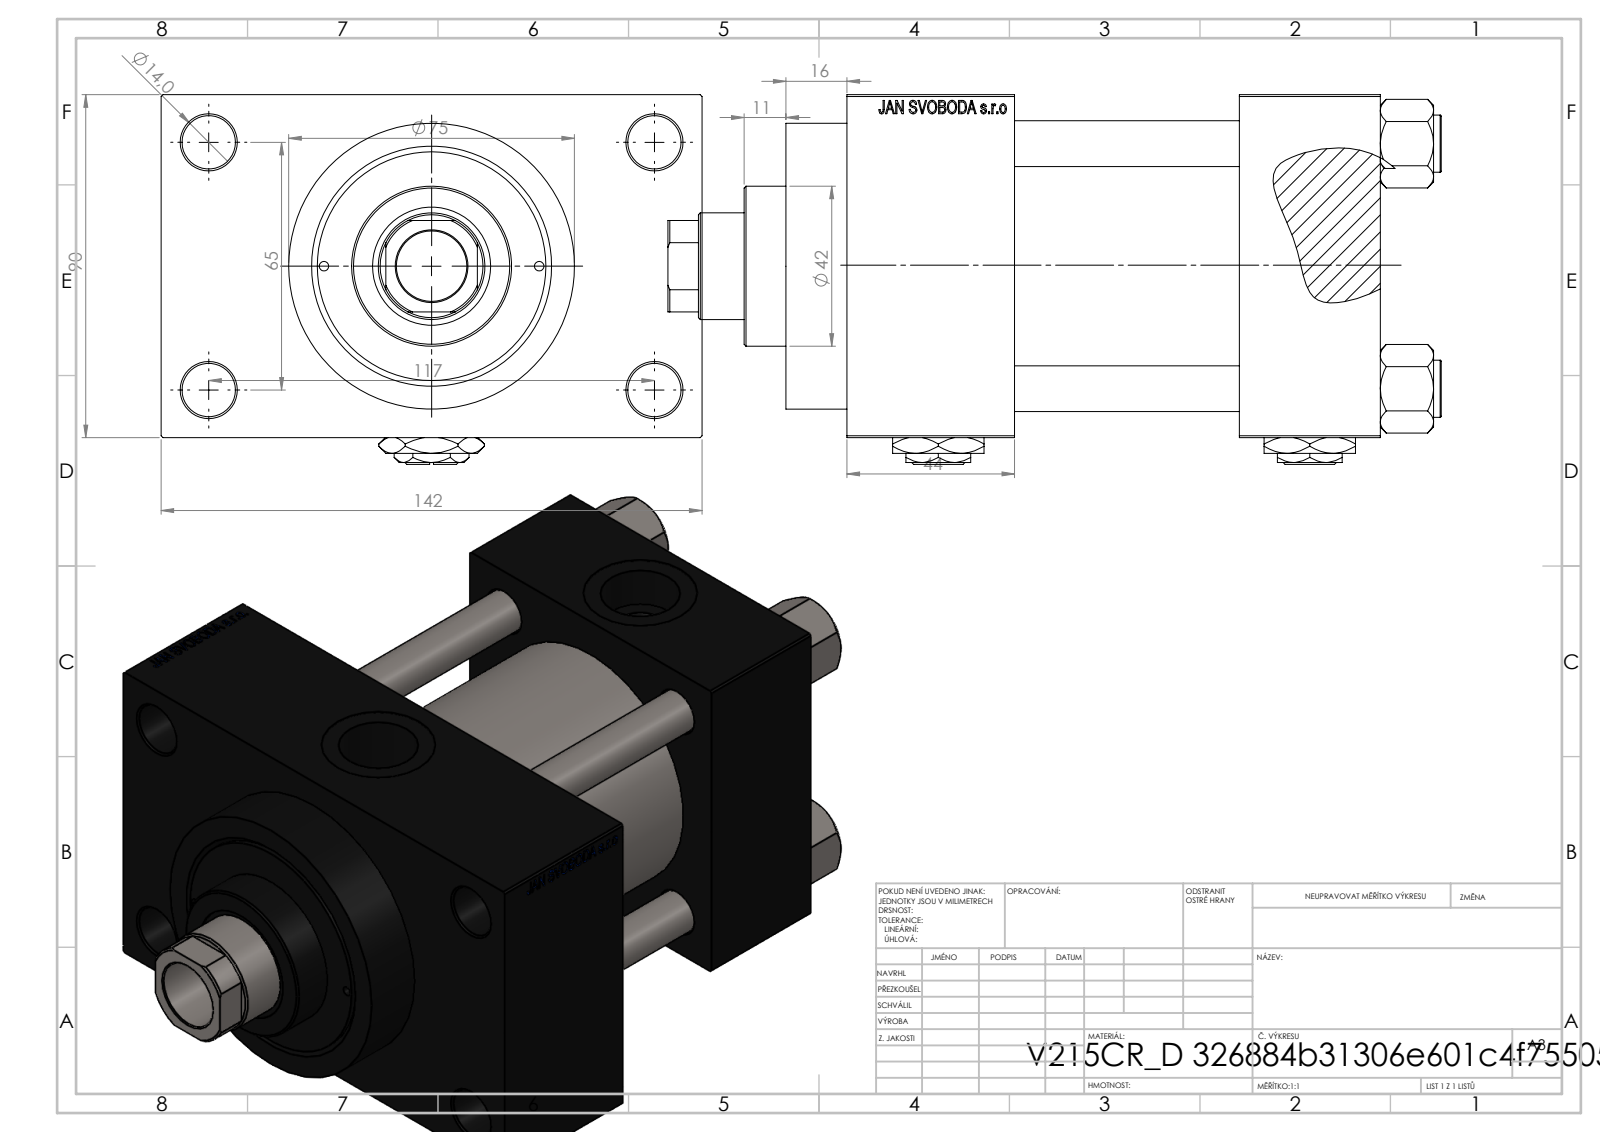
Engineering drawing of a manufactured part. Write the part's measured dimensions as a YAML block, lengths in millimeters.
part_name: "Zatka_pro_OIL_PORT; V215CR_VCP_D; V215CR_D_Body; V215CR_D_TYCINKA (+2 more)"
step_written_by: "SolidWorks 2019 (CONFIG_CONTROL_DESIGN)"
units: millimeters
bodies: {solids: 13, faces: 1213, planar: 547, cylindrical: 104, other: 562}
overall_size: [203, 142, 97]
volume: 1099000
surface_area: 203152
round_holes:
  - {diameter: 12, count: 4}
  - {diameter: 14, count: 4}
  - {diameter: 2.5, count: 2}
  - {diameter: 7, count: 2}
  - {diameter: 20.96, count: 2}
  - {diameter: 30, count: 2}
  - {diameter: 18.5, count: 1}
  - {diameter: 28, count: 1}
  - {diameter: 31, count: 1}
  - {diameter: 50, count: 1}
  - {diameter: 60, count: 1}
  - {diameter: 63, count: 1}
round_bosses_or_shafts:
  - {diameter: 15, count: 4}
  - {diameter: 75, count: 1}
  - {diameter: 69, count: 1}
  - {diameter: 42, count: 1}
partial_cylinders:
  - {radius: 13.5, count: 1}
face_to_face_distances: [90, 59, 37, 96, 140, 103, 44, 26, 116, 142]
hole_center_spacings: [26.35, 32.39, 44.4, 45.47, 64.3, 66.92, 68.42, 69.81]
